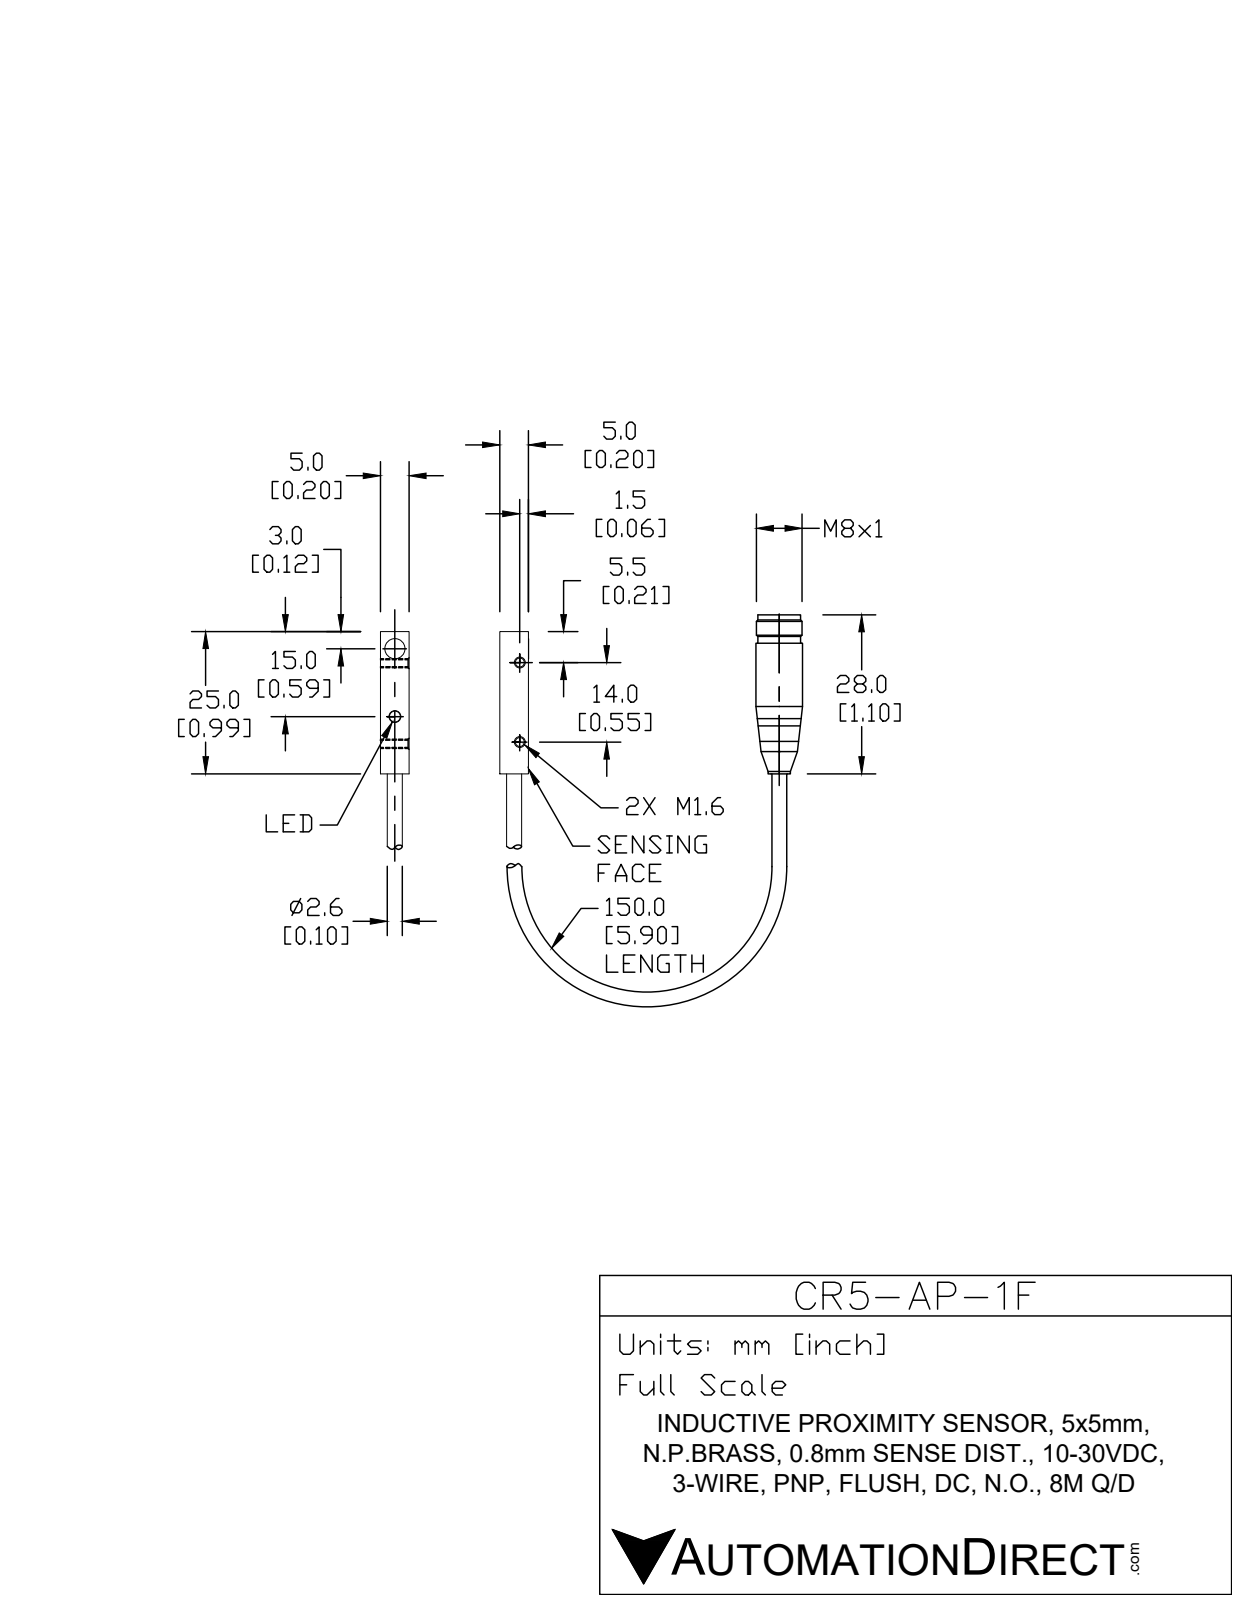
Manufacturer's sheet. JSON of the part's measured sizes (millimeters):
{"part_name": "CR5-AP-1F", "step_written_by": "SolidWorks 2017 (AUTOMOTIVE_DESIGN)", "units": "millimeters", "bodies": {"solids": 2, "faces": 359, "planar": 127, "cylindrical": 84, "other": 148}, "overall_size": [94.8, 10, 10], "volume_mm3": 2590, "surface_area_mm2": 2157, "round_holes": [[1.2, 2], [5.8, 1]], "round_bosses_or_shafts": [[1, 3], [9.8, 1], [8, 1], [7.5, 1], [6.9, 1], [6.5, 1], [2.6, 1]], "partial_cylinders_radius": [[0.2, 8], [5, 1]], "face_to_face_distances": [5, 0.9, 1.8, 2.7, 60, 6.5, 29.8, 89.8, 64.8, 35], "hole_center_spacings": [14]}
